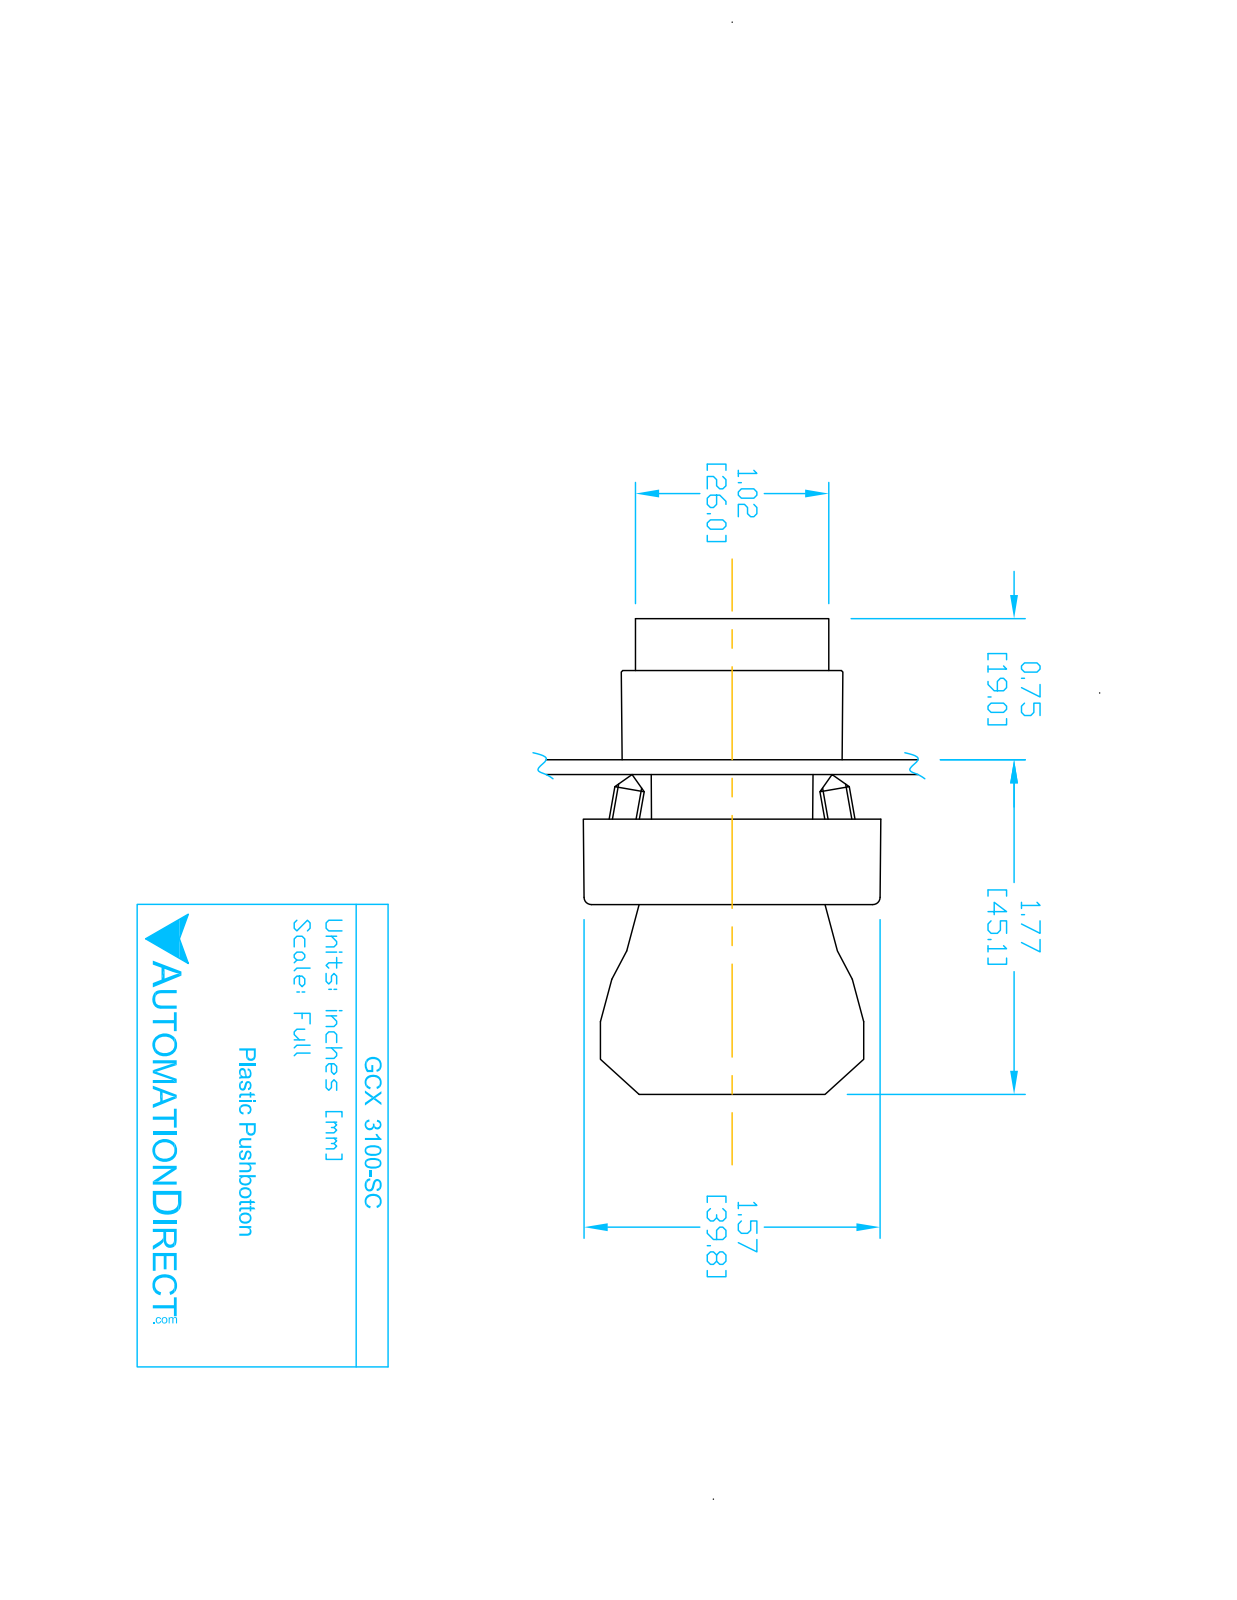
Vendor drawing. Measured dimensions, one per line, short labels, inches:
name: GCX3100 OPERATOR; GCX3100-SC; ECX3029-2
written by: SolidWorks 2016 (AUTOMOTIVE_DESIGN)
unit: in
bodies: 5 solids, 288 faces (147 planar, 118 cylindrical, 23 other)
size: 1.581 × 1.407 × 1.177
volume: 1.09 in³; area: 20.41 in²
holes: 2× ⌀0.124, 2× ⌀0.13, 1× ⌀0.197, 1× ⌀0.878, 1× ⌀0.888, 1× ⌀1.024
bosses: 2× ⌀0.157, 1× ⌀1.175, 1× ⌀1.004, 1× ⌀0.945, 1× ⌀0.856, 1× ⌀0.78
rounds: 24× R0.059, 12× R0.041, 12× R0.124, 12× R0.157, 4× R0.039, 2× R0.128, 1× R0.392, 1× R0.398
face distances: 0.033, 0.72, 1.193, 0.472, 0.031, 0.689, 1.161, 0.122, 0.091, 0.598
